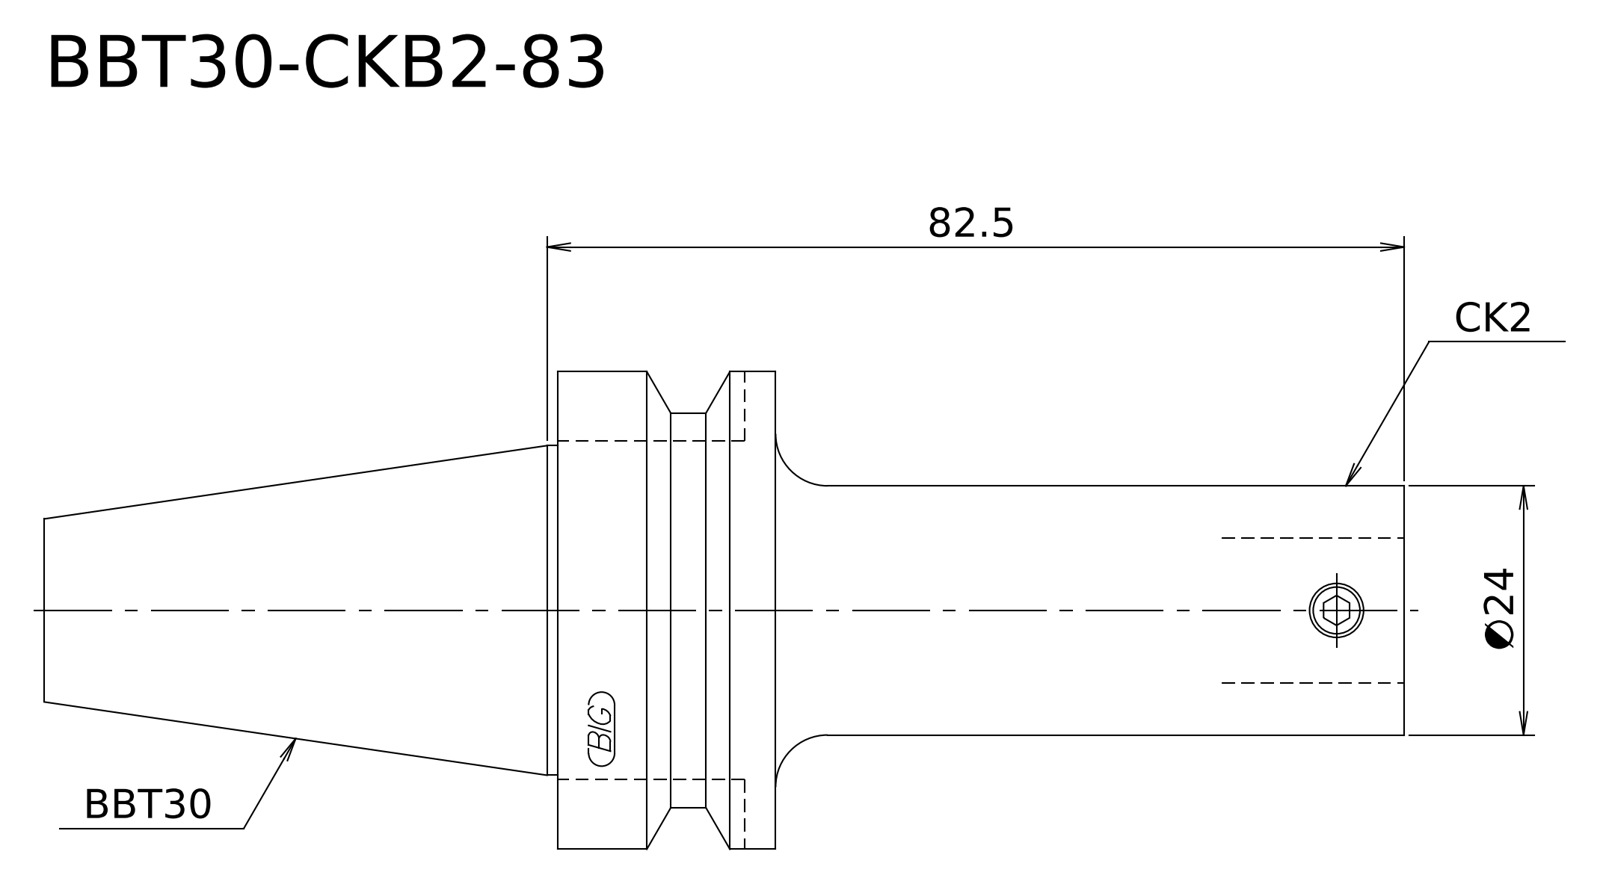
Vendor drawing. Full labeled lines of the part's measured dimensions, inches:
STEP written by: Kubotek KeyCreator V8.5.1 (14335) (CONFIG_CONTROL_DESIGN)
Units: inches
Bodies: 1 solid, 13 faces (4 planar, 5 cylindrical, 4 other)
Overall size (bounding box): 5.154 × 1.811 × 1.811
Volume: 5.181 in³ · Surface area: 22.54 in²
Round bosses / shafts (diameter × count): ⌀1.811 ×1, ⌀1.496 ×1, ⌀1.25 ×1, ⌀0.945 ×1
Main face-to-face distances: 0.827, 2.382, 3.209, 5.154, 2.772, 1.945
